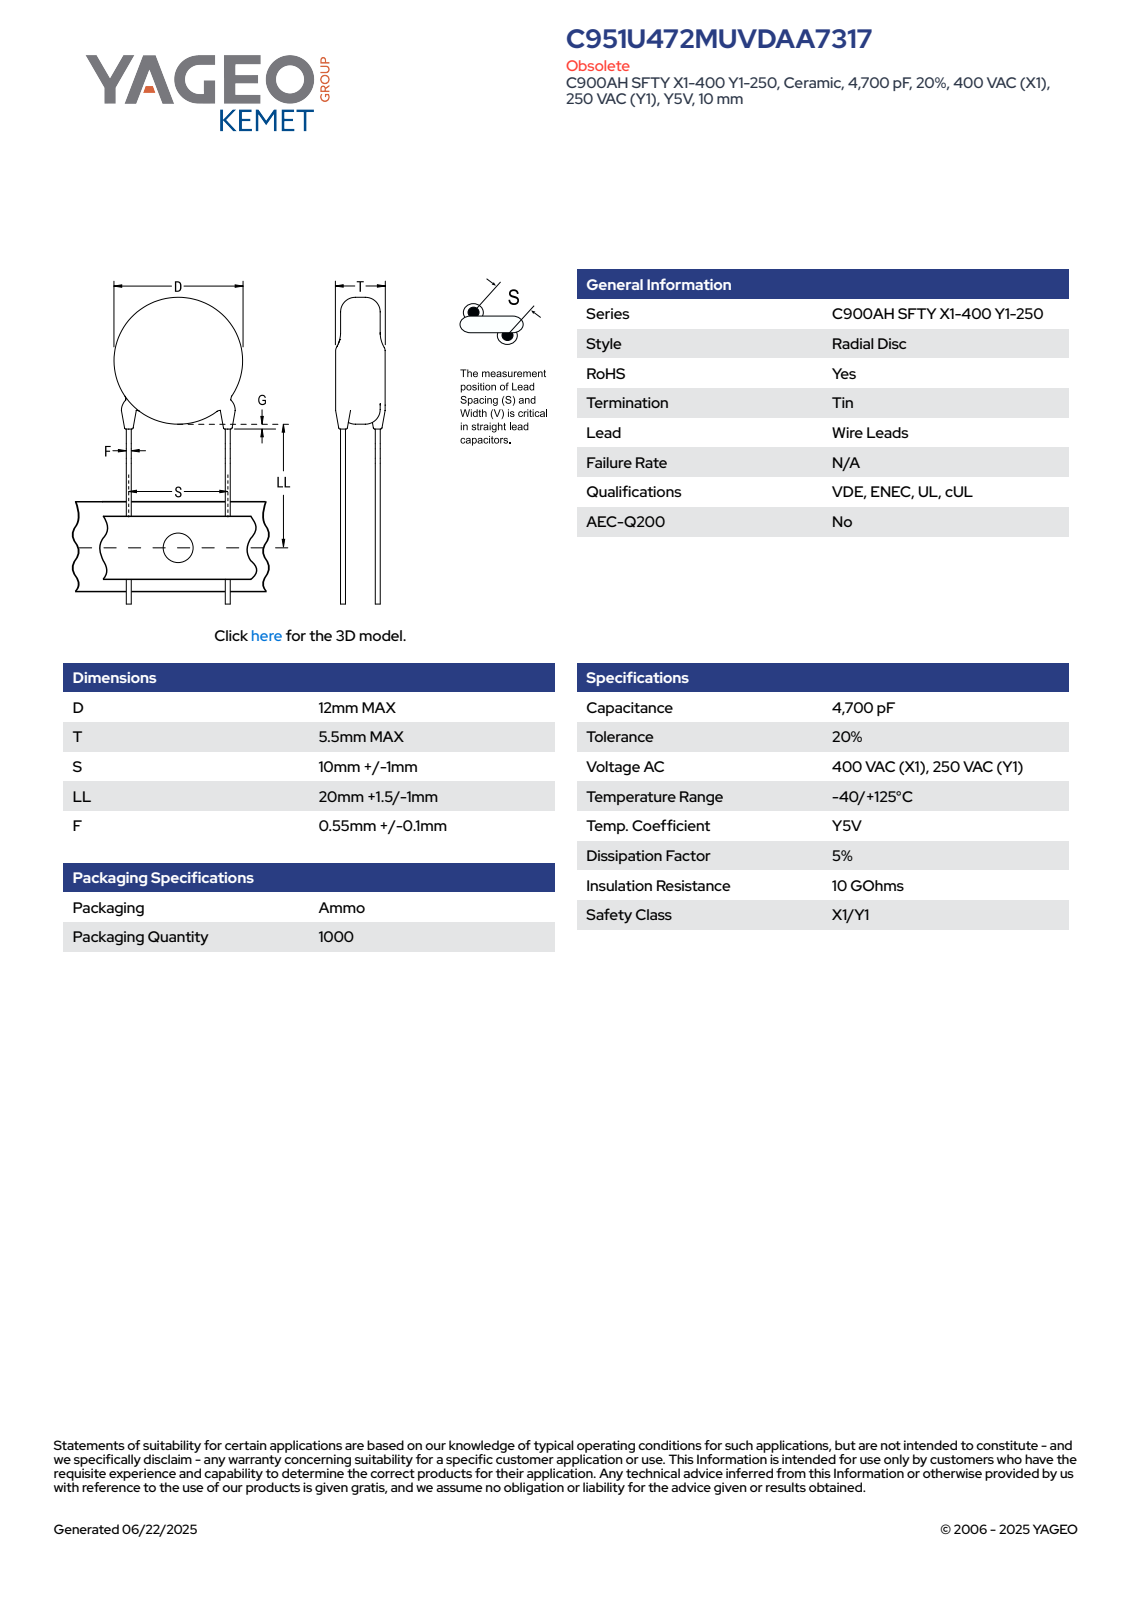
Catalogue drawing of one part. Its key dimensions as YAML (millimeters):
part_name: "CCD_STC900_D12T5.5S10LL21.5F0.65G3"
step_written_by: "SolidWorks 2014 (AUTOMOTIVE_DESIGN)"
units: millimeters
bodies: {solids: 4, faces: 83, planar: 61, cylindrical: 6, other: 16}
overall_size: [33.5, 12, 5.5]
volume: 624
surface_area: 509
round_bosses_or_shafts:
  - {diameter: 0.65, count: 2}
  - {diameter: 12, count: 1}
face_to_face_distances: [5.5, 28.19, 26.81, 1.38, 0.38, 0.34, 0.6, 5.66, 1.12, 0.86]
